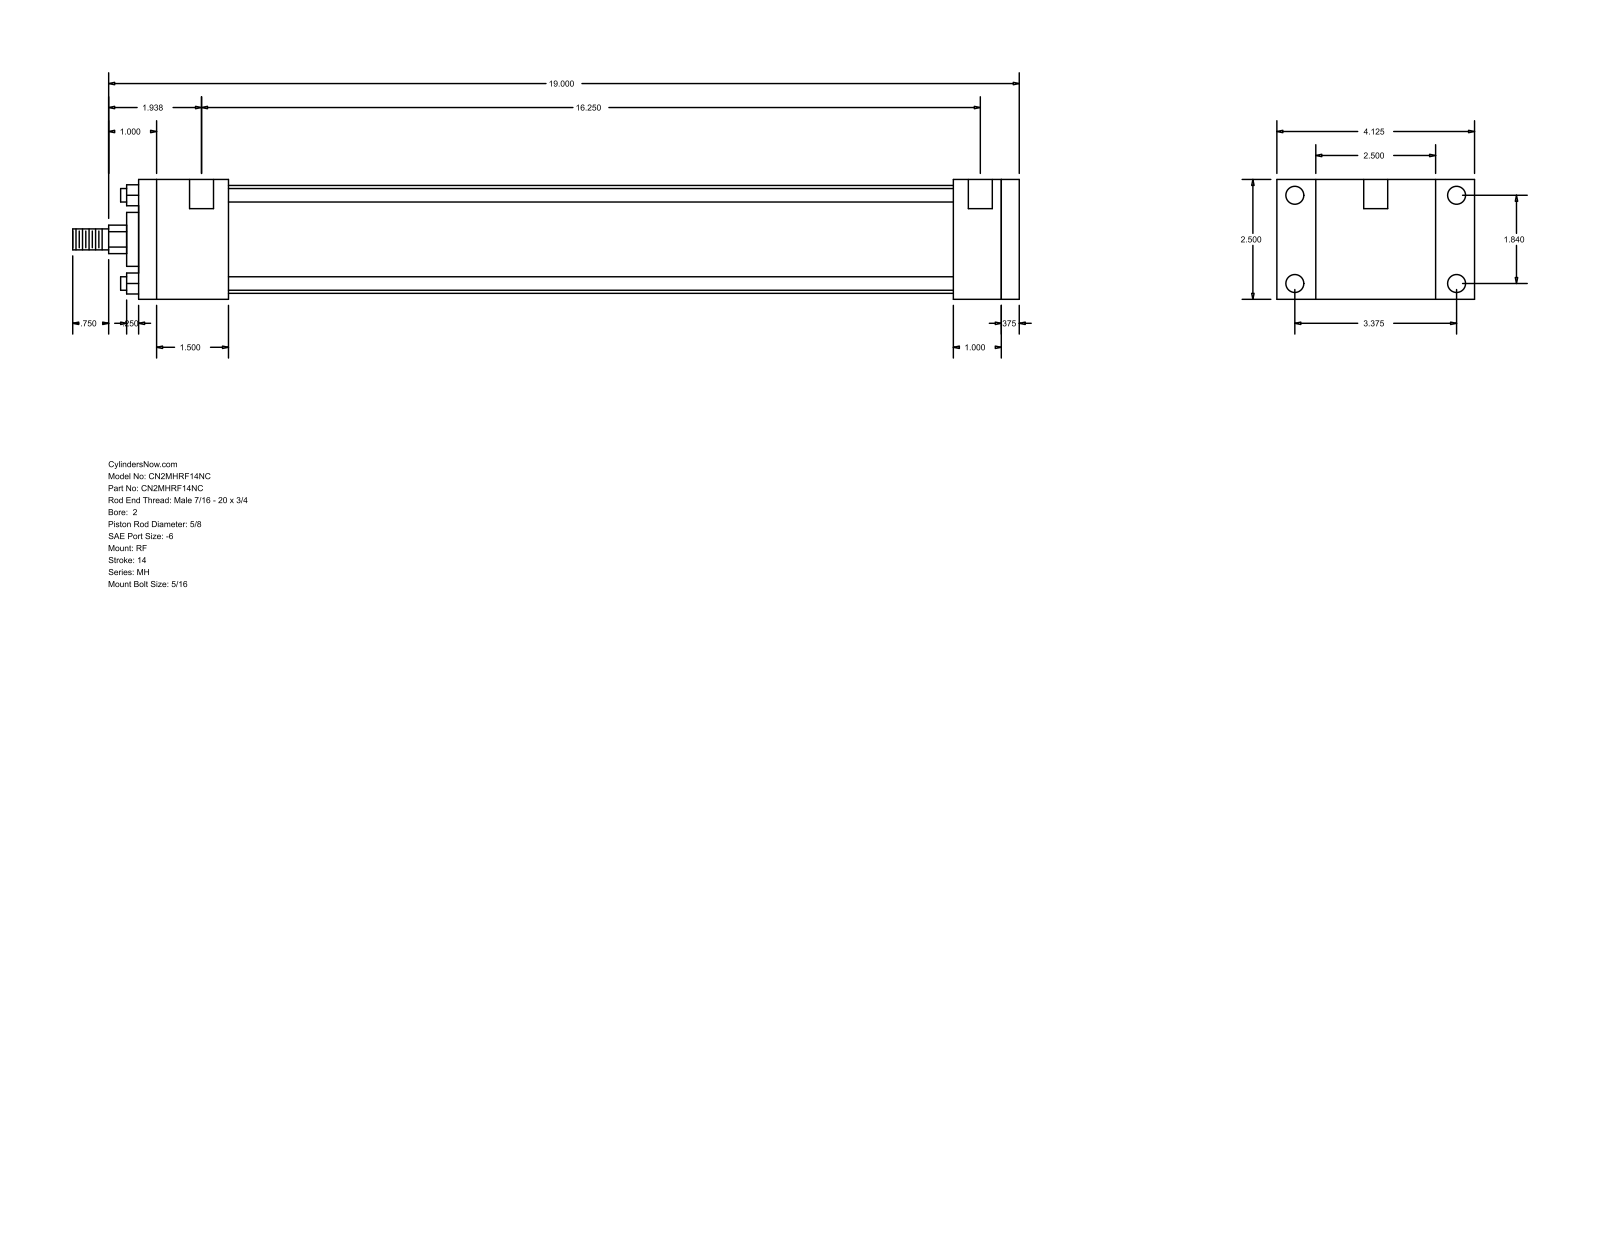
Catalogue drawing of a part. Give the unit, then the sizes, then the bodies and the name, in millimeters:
Units: millimetres
Overall size (bounding box): 501.65 × 104.78 × 63.5
Round holes (diameter × count): ⌀5.56 ×4, ⌀9.53 ×4, ⌀12.7 ×2
Round bosses / shafts (diameter × count): ⌀7.14 ×4, ⌀57.15 ×1, ⌀28.57 ×1, ⌀15.88 ×1, ⌀11.11 ×1
Partial cylindrical surfaces — rounded edges, fillets, slot ends (radius × count): R7.54 ×1
Main face-to-face distances: 63.5, 466.72, 9.53, 457.19, 47.62, 431.8, 384.18, 409.57, 419.1, 25.39
Hole centre spacings: 46.74, 85.72, 97.63, 420.69, 3.18, 4.76, 412.75, 415.93
Bodies: 0 solids, 92 faces (64 planar, 28 cylindrical, 0 other)
Part name (STEP PRODUCT): MH_RF__0200_0.625
STEP written by: GSSL Pune (CONFIG_CONTROL_DESIGN)
